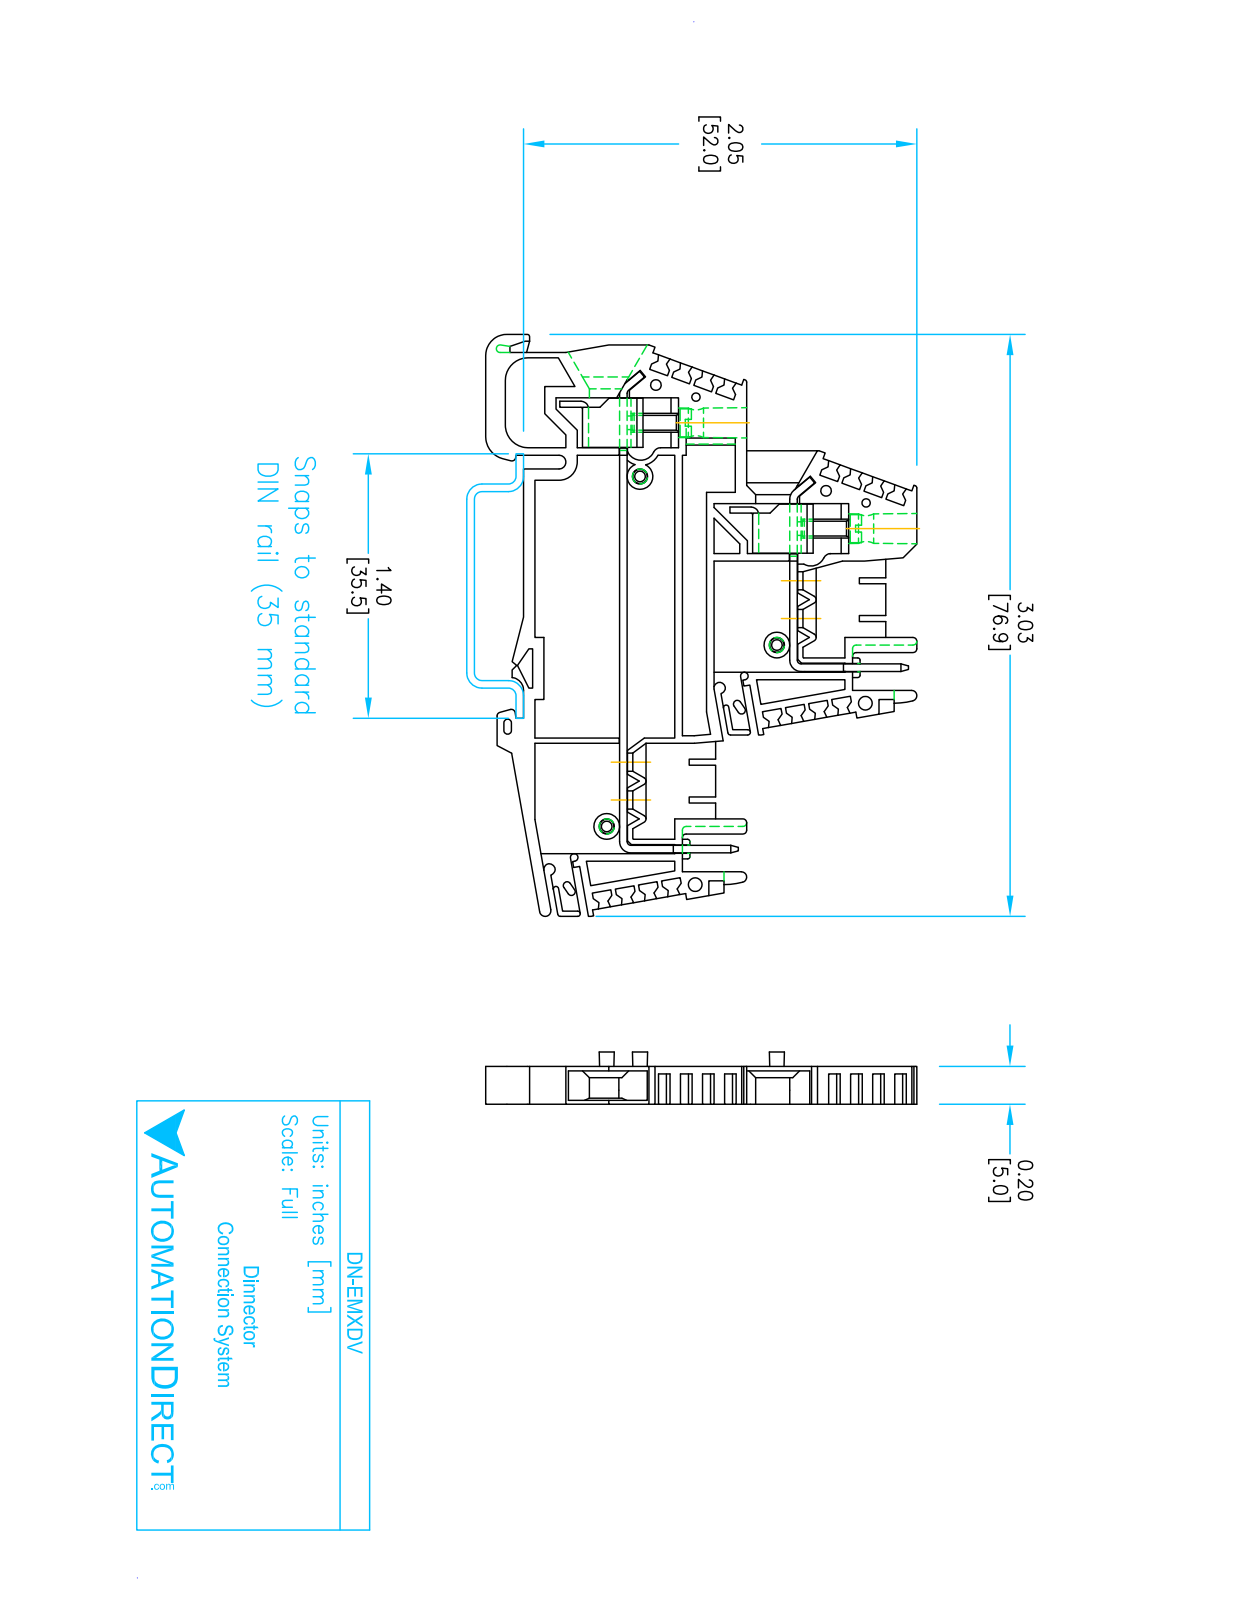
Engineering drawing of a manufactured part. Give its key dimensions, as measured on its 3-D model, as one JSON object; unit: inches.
{"part_name": "20451; 43561_DN-EMXDV", "step_written_by": "SolidWorks 2013 (AUTOMOTIVE_DESIGN)", "units": "inches", "bodies": {"solids": 1, "faces": 475, "planar": 373, "cylindrical": 72, "other": 30}, "overall_size": [3.035, 2.241, 0.272], "volume_in3": 0.678, "surface_area_in2": 14.25, "round_holes": [[0.043, 2], [0.055, 2], [0.071, 2], [0.161, 2], [0.079, 1]], "round_bosses_or_shafts": [[0.102, 2]], "partial_cylinders_radius": [[0.02, 19], [0.118, 5], [0.012, 3], [0.028, 2], [0.03, 2], [0.02, 1], [0.02, 1], [0.035, 1]], "face_to_face_distances": [0.197, 0.169, 0.028, 0.039, 0.118, 0.079, 0.051, 0.087, 0.945, 0.276], "hole_center_spacings": [1.043, 0.218, 0.484, 0.505, 0.539, 0.835, 0.969, 1.125]}
